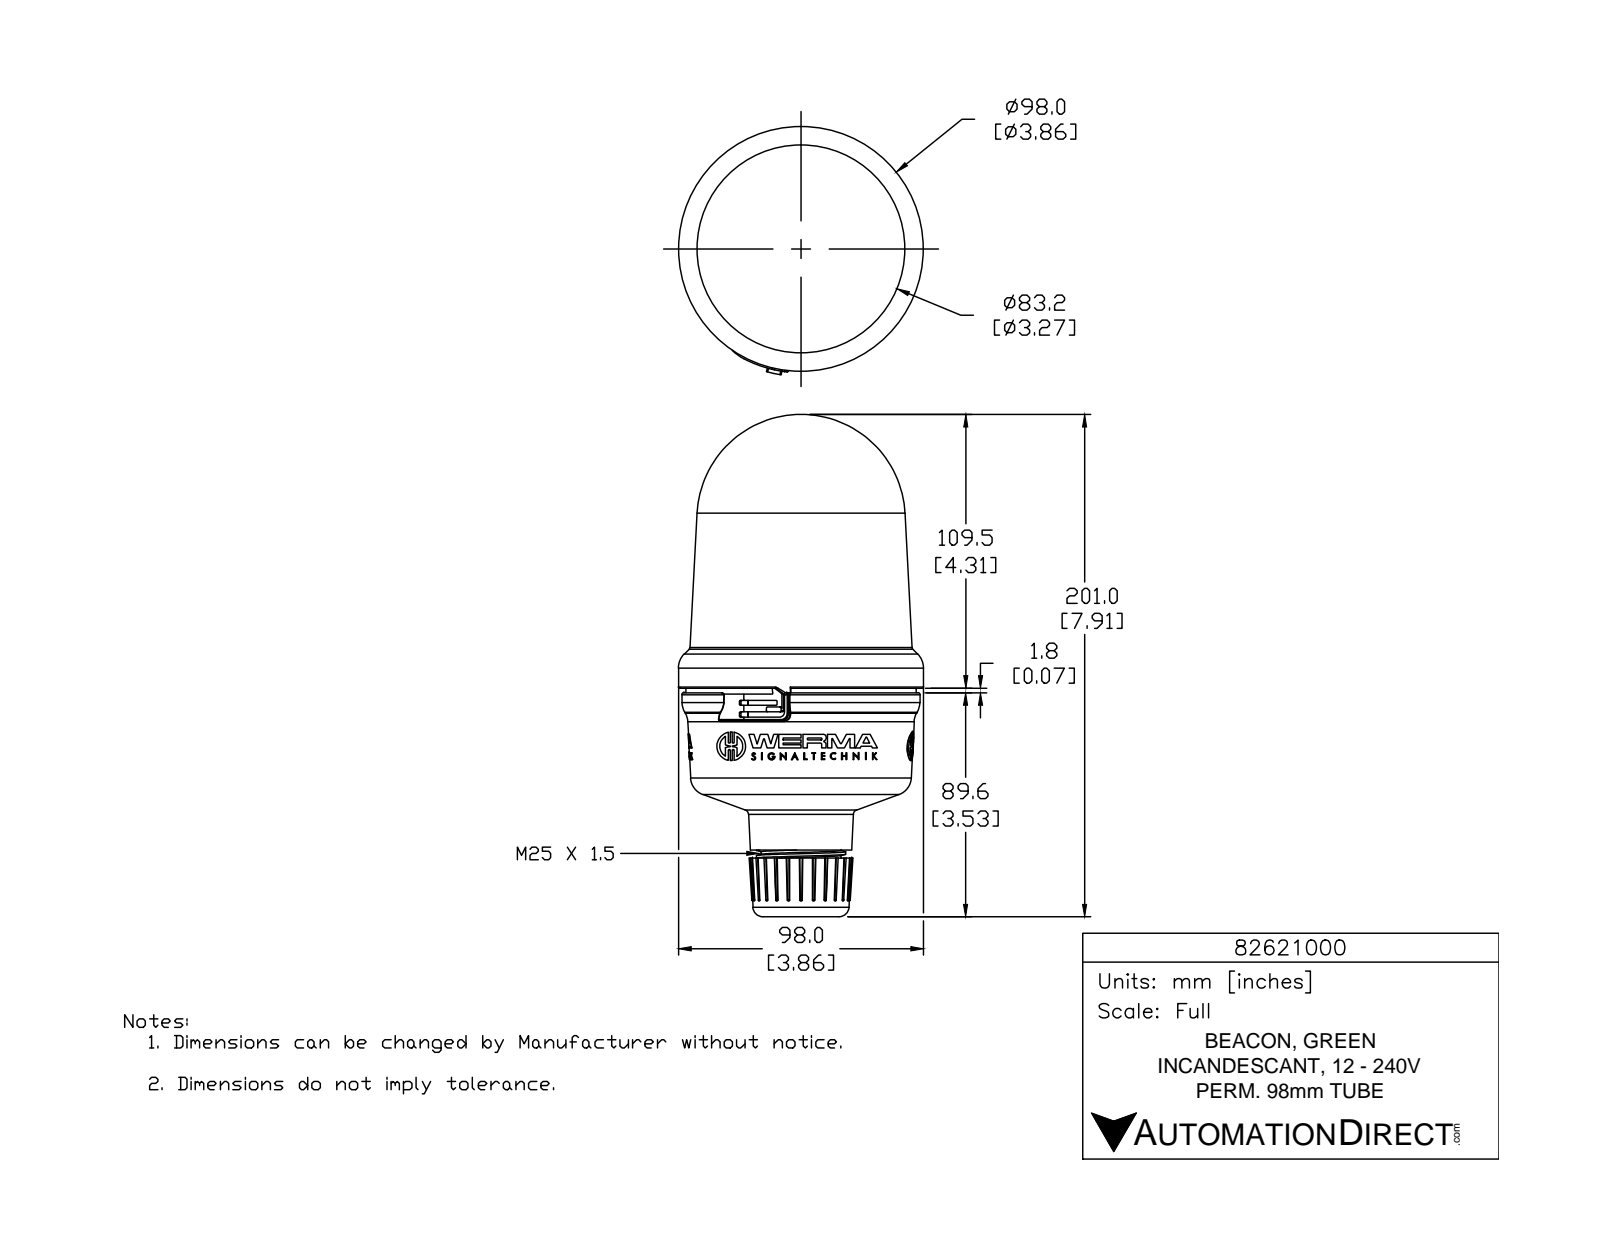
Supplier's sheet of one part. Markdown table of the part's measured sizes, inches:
| quantity | value |
| --- | --- |
| part name | 82621000 |
| STEP written by | SolidWorks 2015 (AUTOMOTIVE_DESIGN) |
| units | inches |
| bodies | 1 solid, 1006 faces (554 planar, 189 cylindrical, 263 other) |
| overall size | 7.914 × 3.912 × 3.858 |
| volume | 54.7 in³ |
| surface area | 91.39 in² |
| round holes (diameter × count) | 0.078 × 3, 1.013 × 1, 1.024 × 1 |
| round bosses / shafts (diameter × count) | 0.452 × 3, 0.113 × 3, 3.858 × 1, 1.409 × 1, 1.261 × 1 |
| partial cylindrical surfaces (radius × count) | 0.02 × 12, 0.007 × 9, 0.007 × 6, 0.016 × 6, 0.016 × 6, 0.016 × 6, 0.262 × 6, 0.006 × 3 |
| main face-to-face distances | 2.214, 0.462, 2.676, 0.335, 0.127, 2.548, 2.603, 2.476, 2.141, 0.073 |
